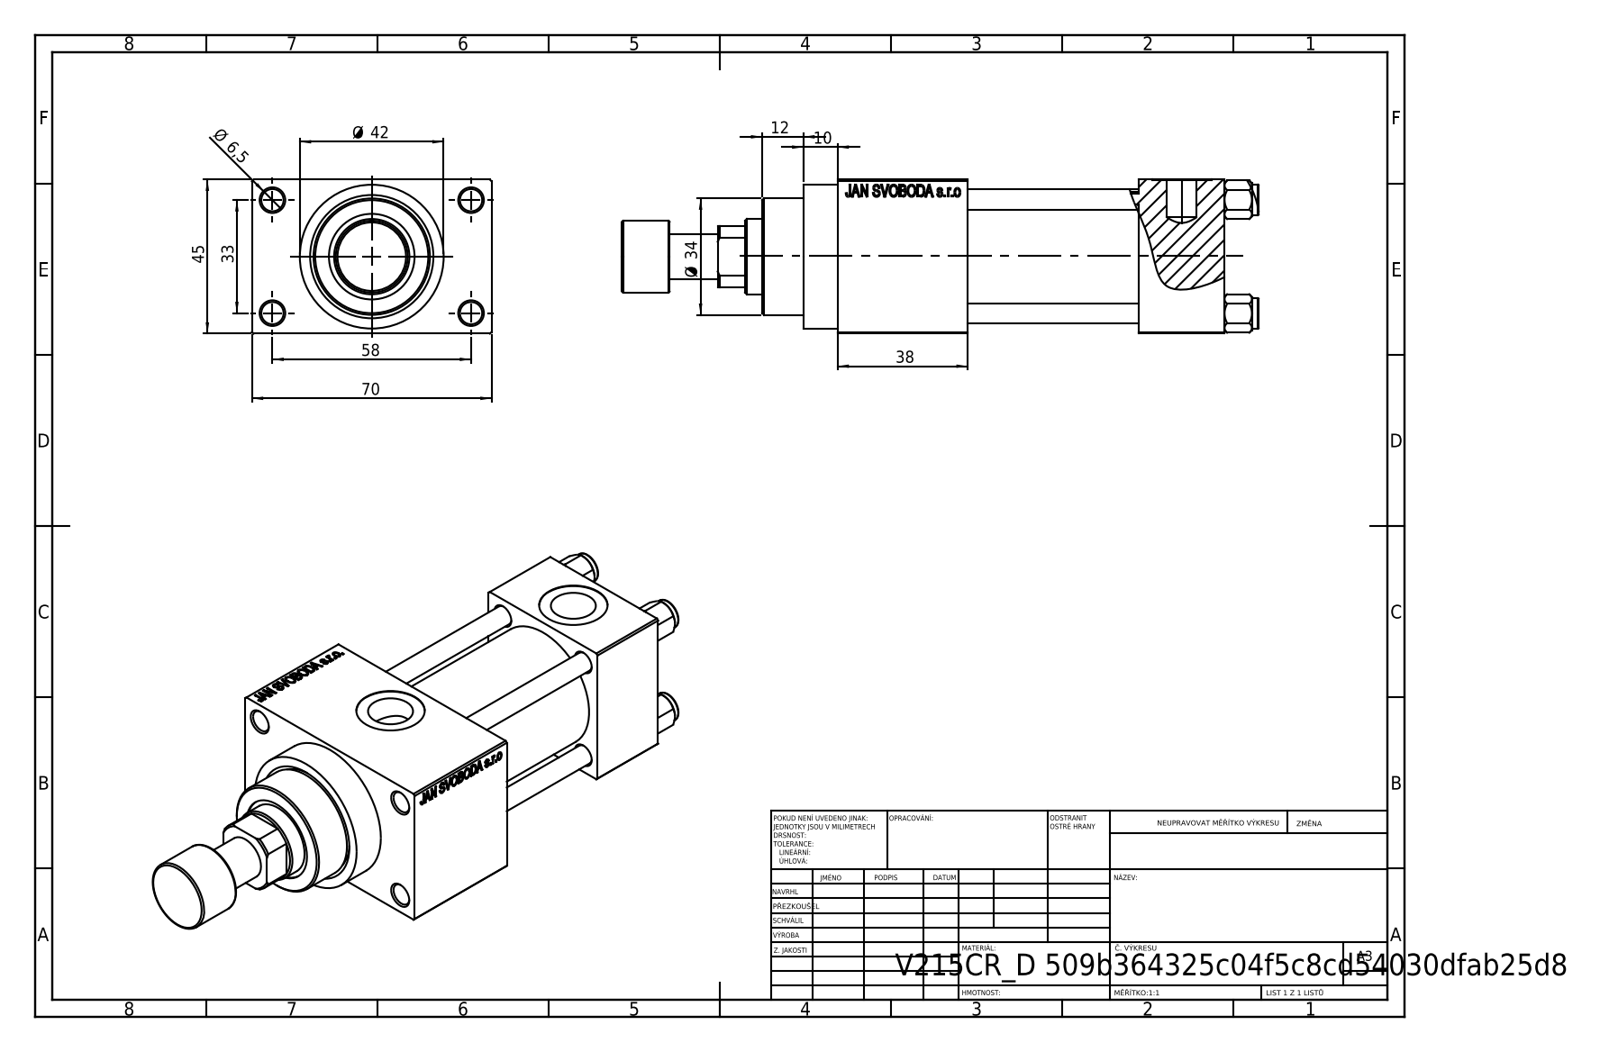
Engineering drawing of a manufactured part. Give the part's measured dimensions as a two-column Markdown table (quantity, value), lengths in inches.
| quantity | value |
| --- | --- |
| part name | V215CR_VCP_D; V215_VC_A; V215CR_ROD_END_F; NUT_M5_D (+2 more) |
| STEP written by | SolidWorks 2019 (CONFIG_CONTROL_DESIGN) |
| units | inches |
| bodies | 12 solids, 1116 faces (499 planar, 93 cylindrical, 524 other) |
| overall size | 7.323 × 2.756 × 1.772 |
| volume | 15.33 in³ |
| surface area | 126.4 in² |
| round holes (diameter × count) | 0.236 × 4, 0.256 × 4, 0.276 × 2, 0.518 × 2, 0.787 × 2, 0.413 × 1, 0.866 × 1, 0.945 × 1, 0.984 × 1, 1.26 × 1, 1.299 × 1 |
| round bosses / shafts (diameter × count) | 0.354 × 4, 1.654 × 1, 1.496 × 1, 1.339 × 1, 0.827 × 1, 0.512 × 1 |
| main face-to-face distances | 1.772, 0.984, 0.492, 2.264, 1.969, 2.953, 3.465, 2.756, 1.496, 4.449 |
| hole center spacings | 0.488, 0.924, 1.307, 1.314, 1.392, 1.795, 2.219, 1.299 |
